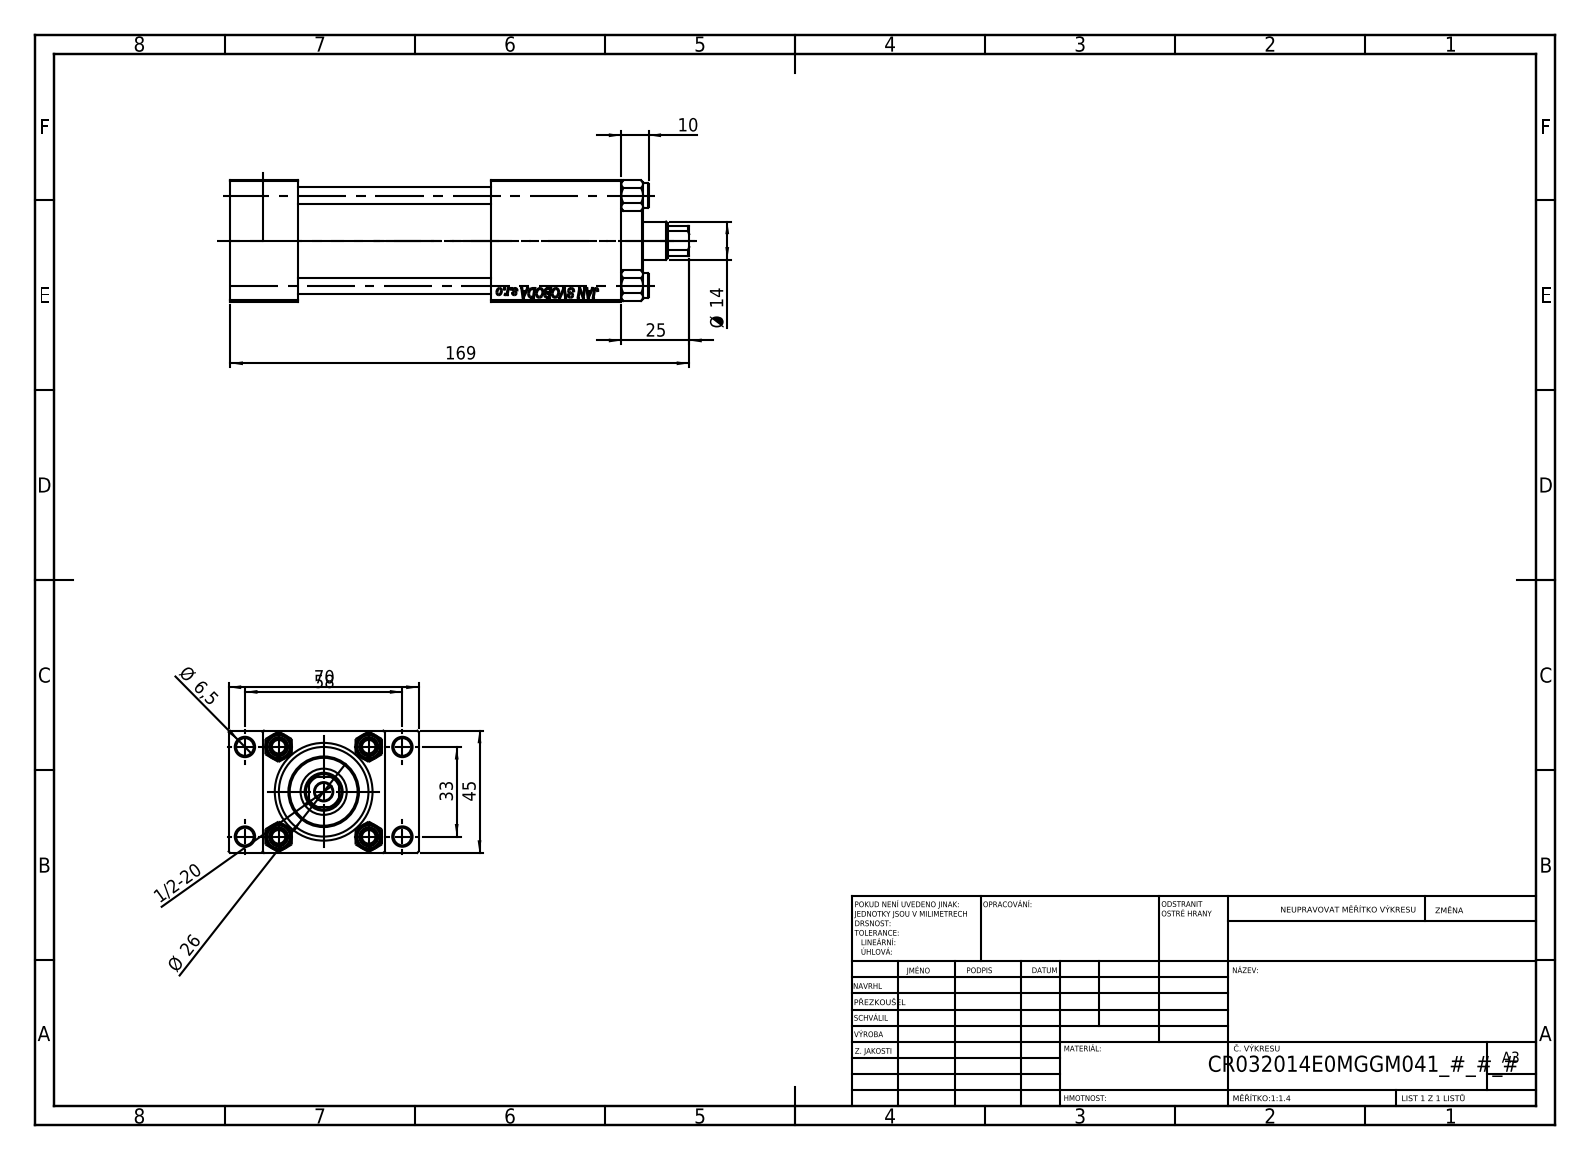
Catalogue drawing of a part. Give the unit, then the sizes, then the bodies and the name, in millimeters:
Units: millimetres
Overall size (bounding box): 169 × 70 × 45
Round holes (diameter × count): ⌀6.5 ×5, ⌀6 ×4, ⌀7 ×2, ⌀13.16 ×2, ⌀20 ×2, ⌀14 ×1, ⌀17 ×1, ⌀24 ×1, ⌀32 ×1, ⌀33 ×1
Round bosses / shafts (diameter × count): ⌀9 ×4, ⌀38 ×1, ⌀26 ×1
Partial cylindrical surfaces — rounded edges, fillets, slot ends (radius × count): R6.5 ×1
Main face-to-face distances: 45, 25, 12.5, 57.5, 144, 119, 70, 96, 71, 48
Hole centre spacings: 12.4, 23.48, 33.2, 33.37, 35.35, 45.6, 56.35, 33
Volume: 232 608 mm³ · Surface area: 83 198 mm²
Bodies: 11 solids, 1136 faces (497 planar, 87 cylindrical, 552 other)
Part name (STEP PRODUCT): V215CR_TYCINKA_E; V215CR_E_Body; V215CR_VCP_E; V215_VC_A (+1 more)
STEP written by: SolidWorks 2019 (CONFIG_CONTROL_DESIGN)
